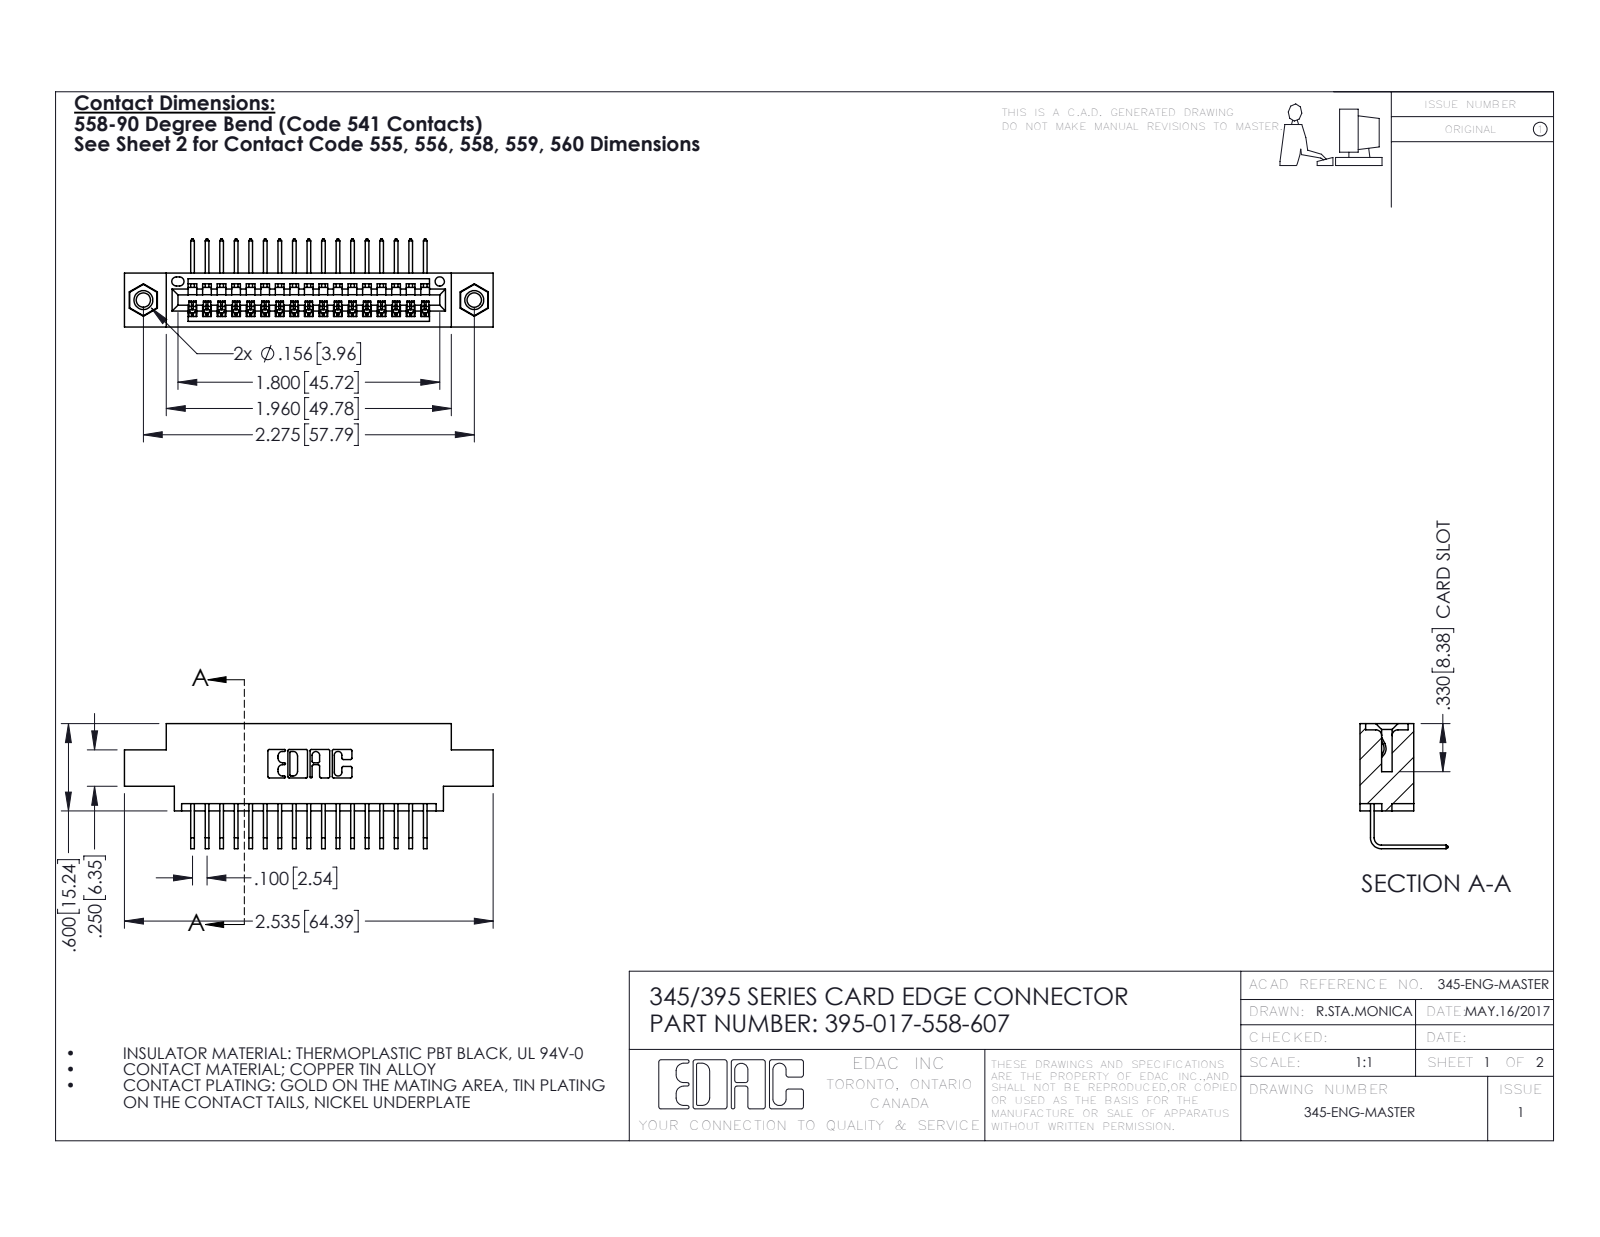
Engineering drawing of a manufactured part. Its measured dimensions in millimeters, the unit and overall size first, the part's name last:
Units: millimetres
Overall size (bounding box): 64.4 × 21.8 × 15.4
Round holes (diameter × count): ⌀2.5 ×2, ⌀3.2 ×2, ⌀4 ×2, ⌀1.6 ×1
Round bosses / shafts (diameter × count): ⌀3.9 ×2
Partial cylindrical surfaces — rounded edges, fillets, slot ends (radius × count): R0.2 ×34, R0.3 ×22, R0.2 ×6, R0.8 ×6, R0.7 ×3, R0.8 ×2, R1 ×2, R0.4 ×1
Main face-to-face distances: 1.8, 7.6, 9.4, 5.1, 2.5, 6.9, 0.6, 5.7, 2.5, 3.8
Hole centre spacings: 6.9, 51.8, 57.8
Volume: 5 830 mm³ · Surface area: 7 916 mm²
Bodies: 20 solids, 1210 faces (830 planar, 364 cylindrical, 16 other)
Part name (STEP PRODUCT): 395-017-558-607; 345 Part_0.170 Offset - 0.156 Dia-TI; 345-250-001_345-250-005-103; 345-292-001_558 Tail - 2
STEP written by: SolidWorks 2016 (CONFIG_CONTROL_DESIGN)
